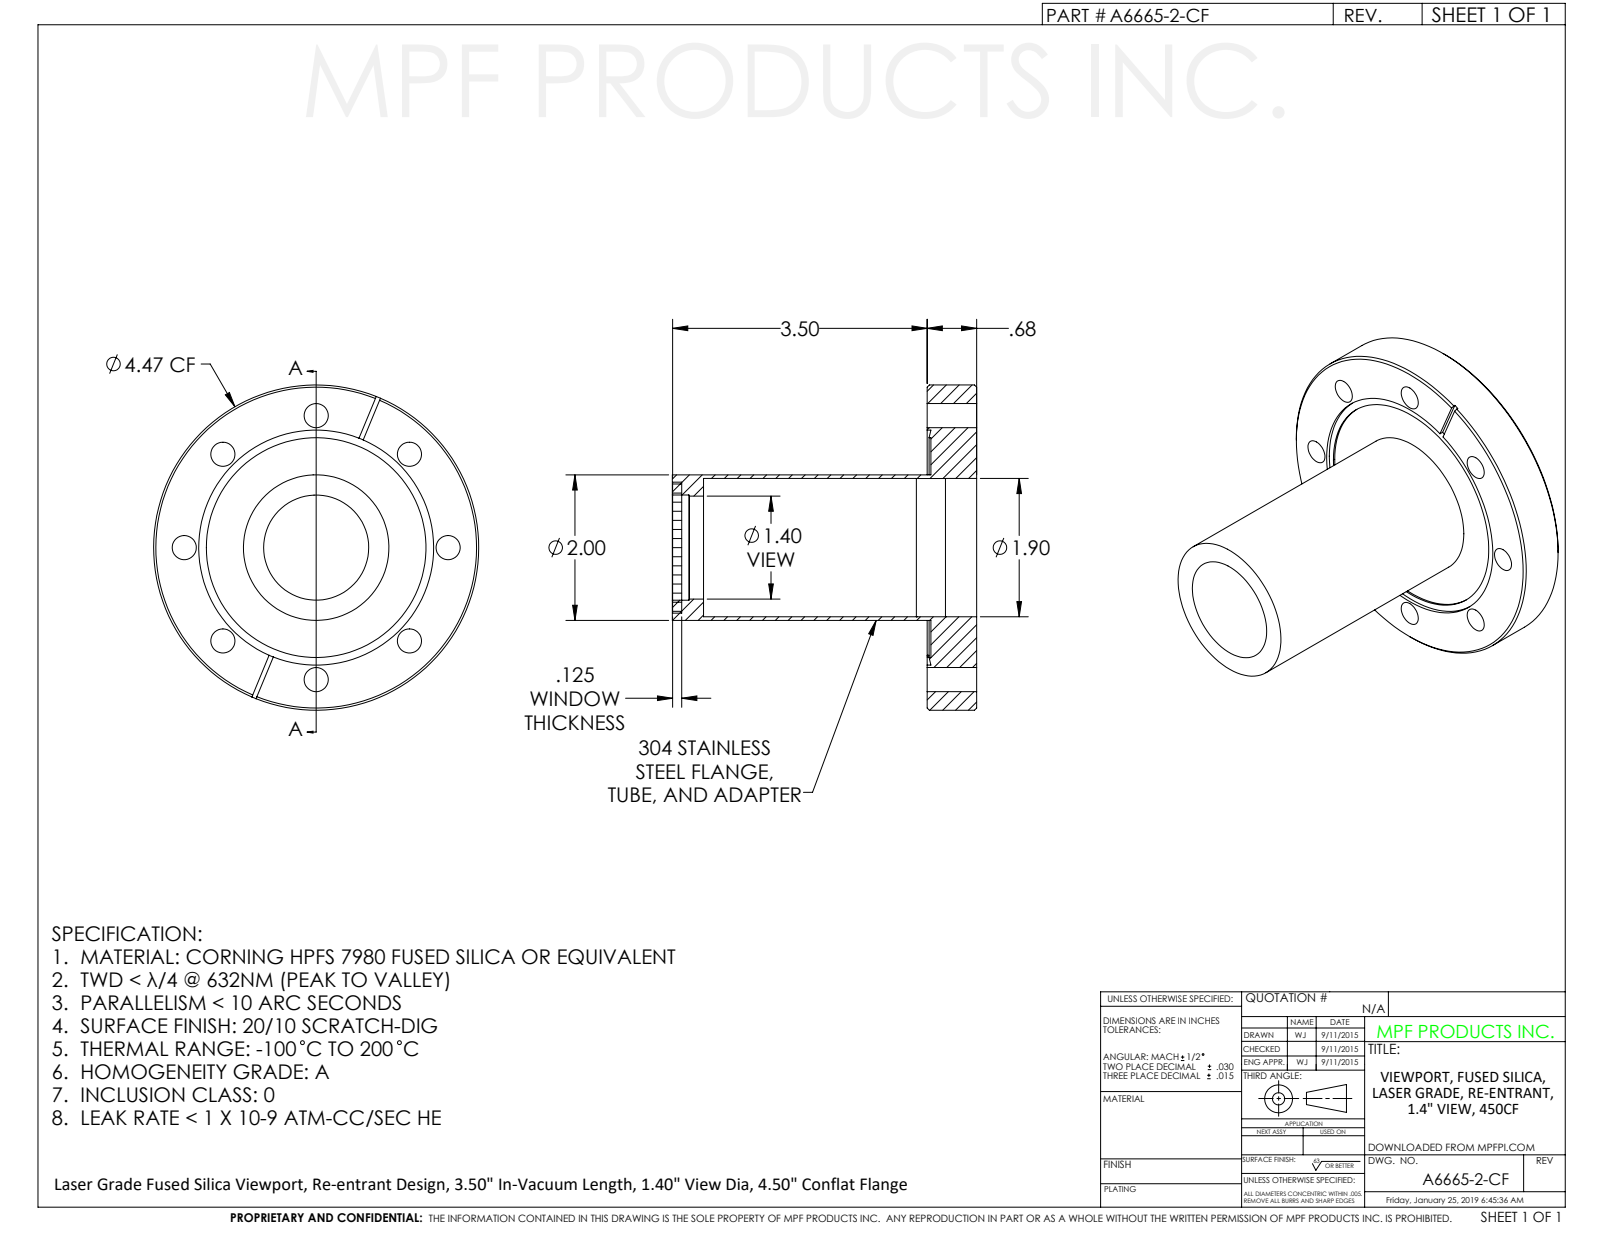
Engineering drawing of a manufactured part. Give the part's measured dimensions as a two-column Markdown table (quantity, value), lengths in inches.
| quantity | value |
| --- | --- |
| part name | A6665-2-CF |
| STEP written by | SolidWorks 2011 (CONFIG_CONTROL_DESIGN) |
| units | inches |
| bodies | 1 solid, 72 faces (14 planar, 44 cylindrical, 14 other) |
| overall size | 4.47 × 4.47 × 4.18 |
| volume | 9.614 in³ |
| surface area | 98.35 in² |
| round holes (diameter × count) | 0.332 × 8, 1.42 × 1, 1.745 × 1, 1.8 × 1, 1.902 × 1, 2.16 × 1, 3.02 × 1, 3.23 × 1 |
| round bosses / shafts (diameter × count) | 4.47 × 1, 2.035 × 1, 2 × 1, 1.896 × 1, 1.765 × 1, 1.48 × 1, 1.44 × 1 |
| main face-to-face distances | 0.68, 0.629, 0.051, 4.18, 3.551, 3.5, 4.055, 3.426, 3.375, 0.125 |
| hole center spacings | 1.389, 1.814, 3.352, 2.565, 2.566, 3.628, 3.628 |
